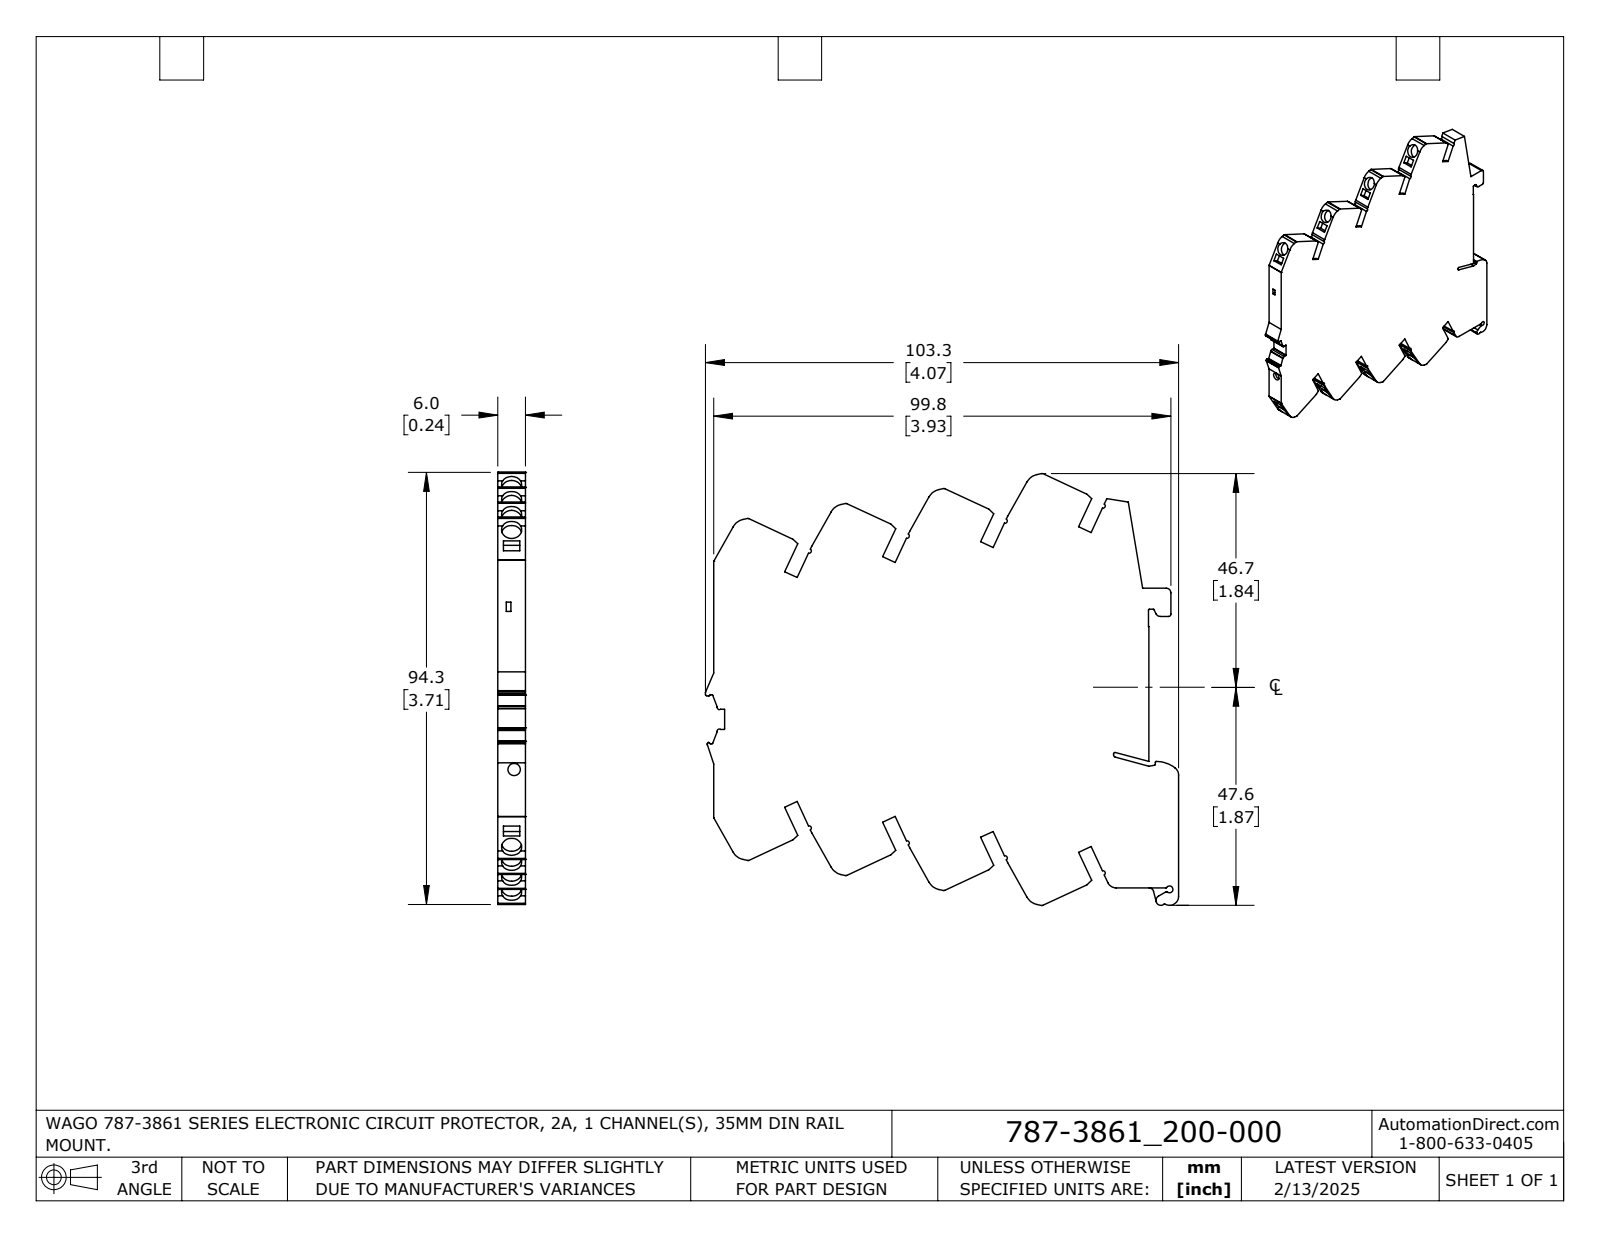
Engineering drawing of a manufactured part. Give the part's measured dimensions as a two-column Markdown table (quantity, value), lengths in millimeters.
| quantity | value |
| --- | --- |
| part name | 787-3861_200-000_HI |
| STEP written by | SolidWorks 2024 (AUTOMOTIVE_DESIGN) |
| units | millimeters |
| bodies | 1 solid, 262 faces (197 planar, 65 cylindrical, 0 other) |
| overall size | 103.3 × 94.26 × 6 |
| volume | 43 992 mm³ |
| surface area | 18 864 mm² |
| round holes (diameter × count) | 4.4 × 8, 2.7 × 1 |
| partial cylindrical surfaces (radius × count) | 0.2 × 13, 0.5 × 12, 0.4 × 8, 3.35 × 8, 1 × 5, 0.3 × 3, 2 × 3, 0.45 × 2 |
| main face-to-face distances | 6, 17.99, 17.02, 12.01, 3, 35.98, 12, 24.01, 14.99, 34.04 |
| hole center spacings | 13.35, 13.34, 26.7, 26.71, 40.05 |
